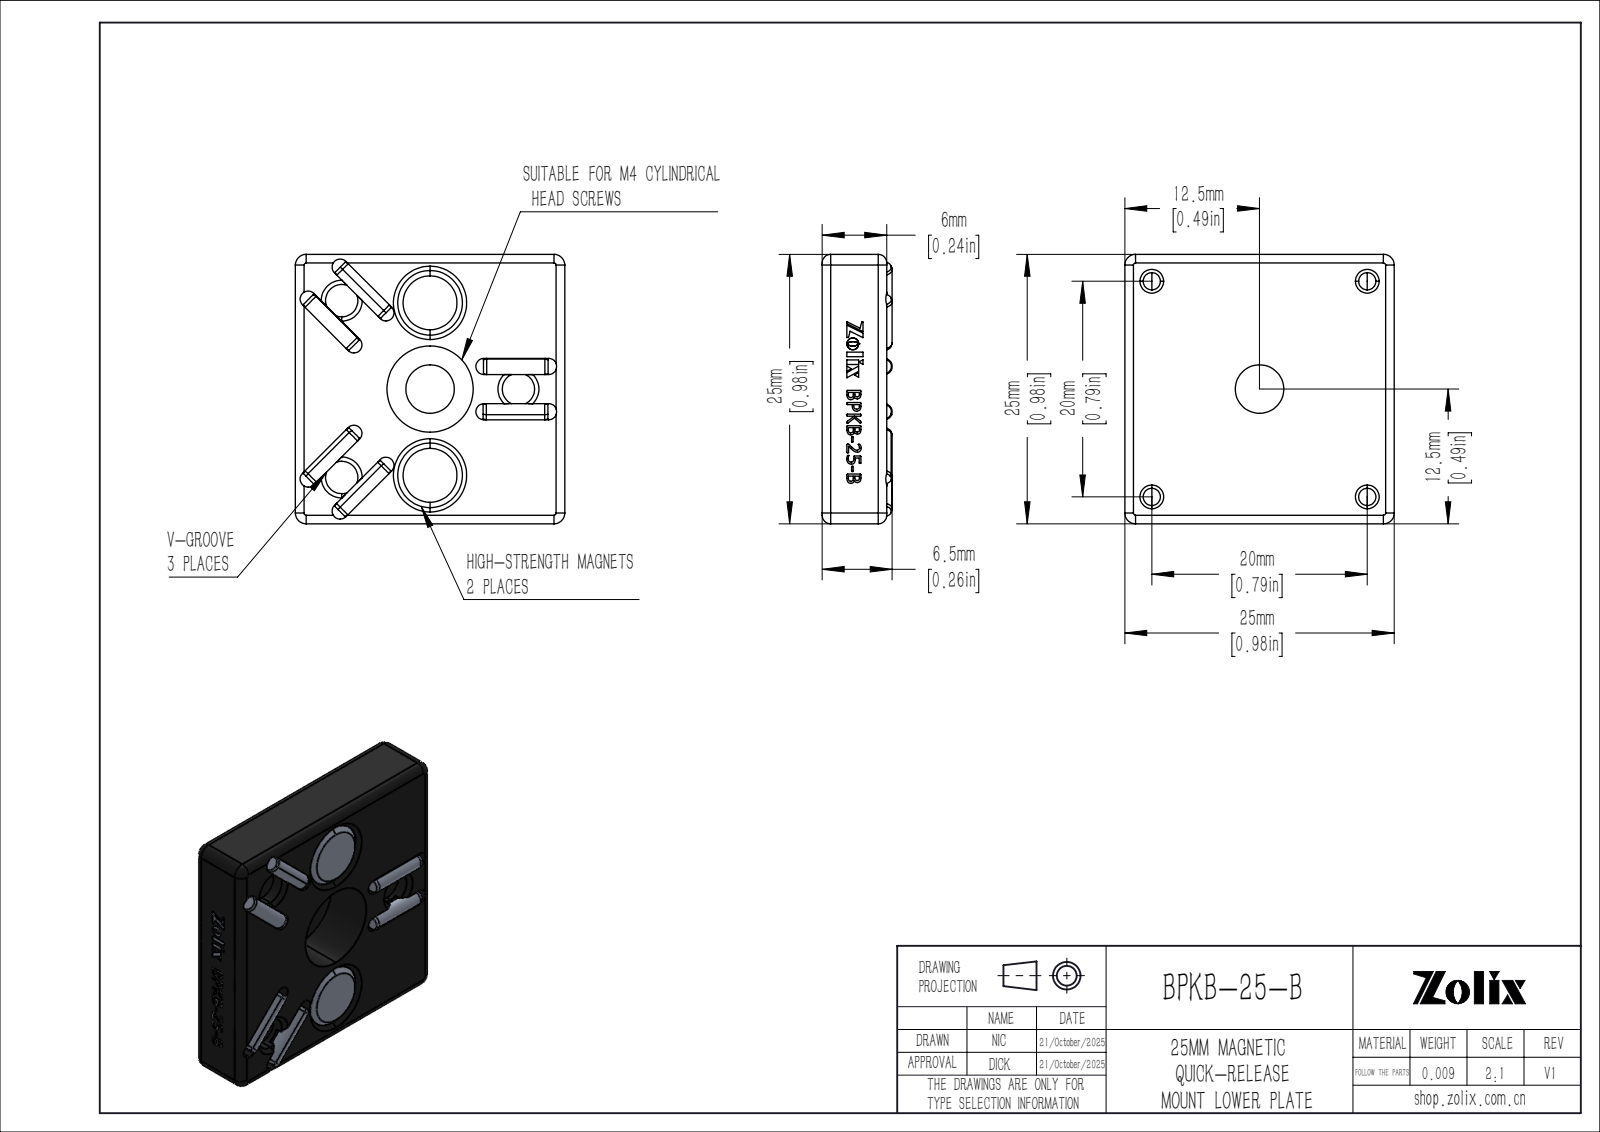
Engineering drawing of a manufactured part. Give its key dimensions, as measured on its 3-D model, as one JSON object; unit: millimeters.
{"part_name": "BPKB-25-B", "step_written_by": "SolidWorks 2020 (CONFIG_CONTROL_DESIGN)", "units": "millimeters", "bodies": {"solids": 9, "faces": 510, "planar": 297, "cylindrical": 66, "other": 147}, "overall_size": [25, 25, 6.5], "volume_mm3": 3374, "surface_area_mm2": 2591, "round_holes": [[1.6, 4], [3, 3], [6, 2], [4.5, 1], [8, 1]], "round_bosses_or_shafts": [[1.5, 6]], "partial_cylinders_radius": [[0.75, 12], [0.8, 8], [1, 4]], "face_to_face_distances": [6, 25, 3, 1.5, 1, 5, 2, 1.4, 3.6, 1.6], "hole_center_spacings": [10.2, 14.14, 18.29, 20, 20.59, 8.2, 2.55, 8]}
